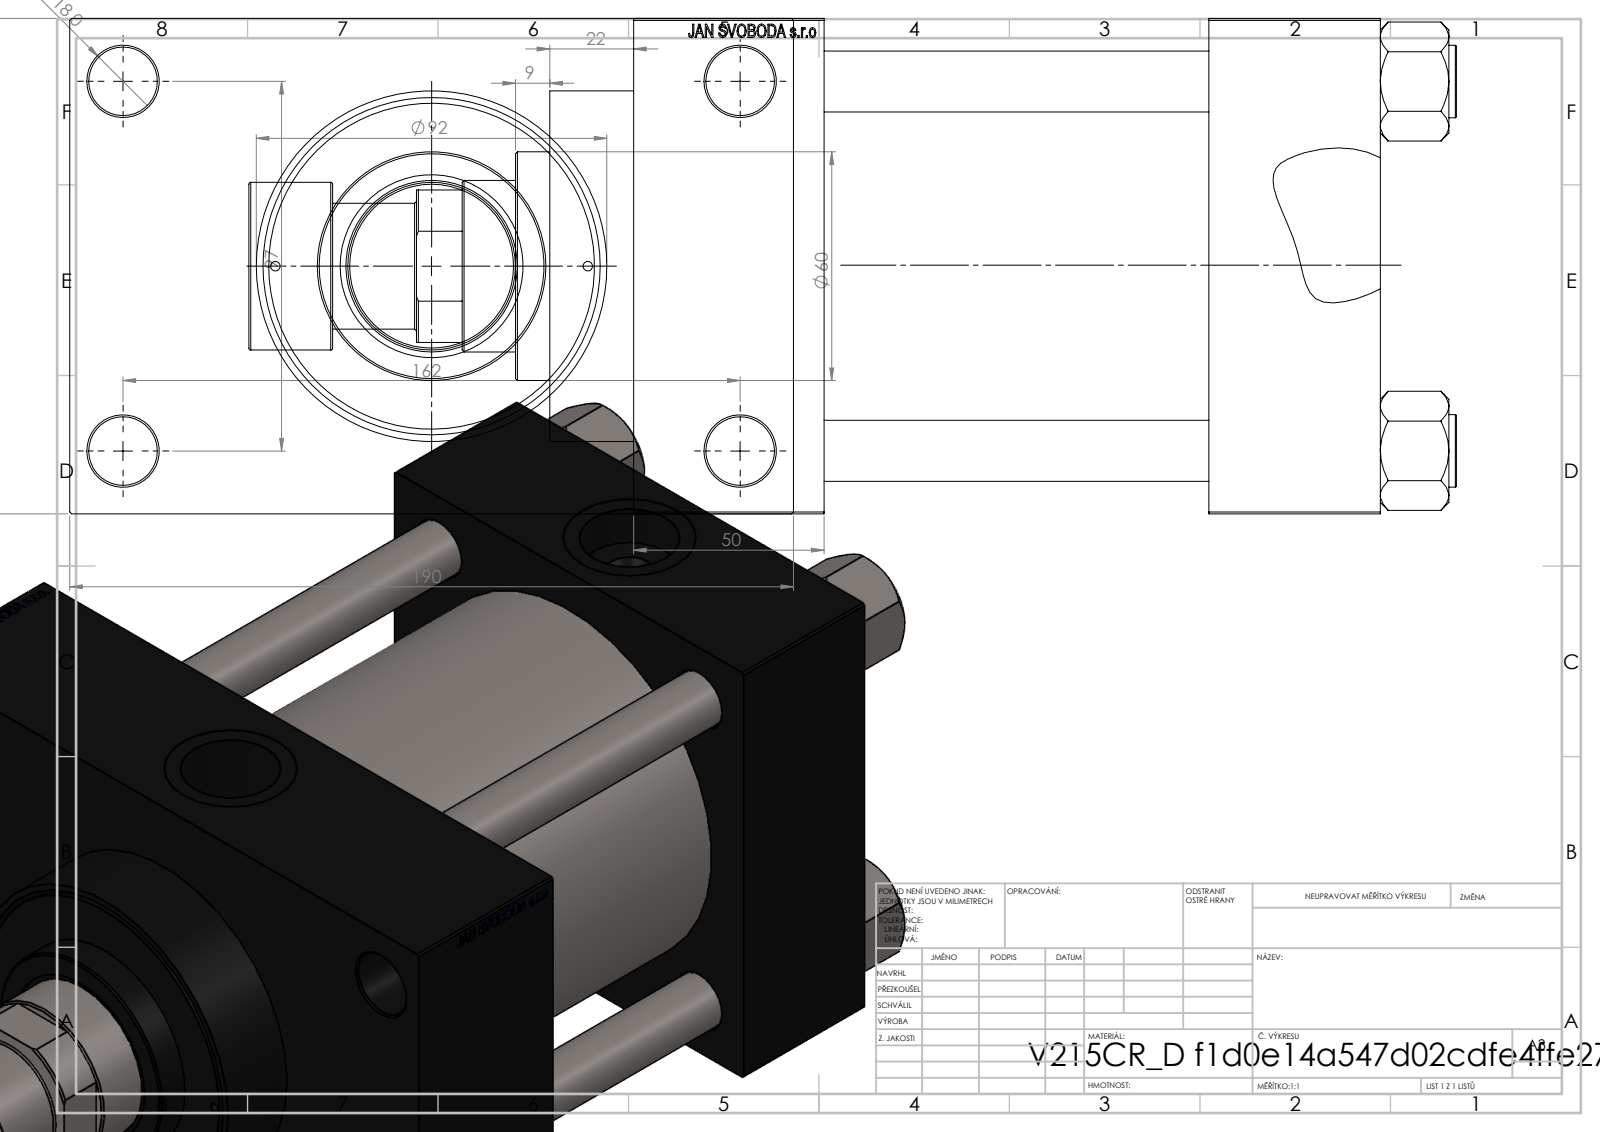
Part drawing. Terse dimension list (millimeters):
name: V215CR_ROD_END_F; V215CR_VCP_D; NUT_M5_D; V215CR_D_Body (+2 more)
written by: SolidWorks 2019 (CONFIG_CONTROL_DESIGN)
unit: mm
bodies: 12 solids, 1173 faces (550 planar, 97 cylindrical, 526 other)
size: 317 × 190 × 130
volume: 2 760 000 mm³; area: 390 306 mm²
holes: 4× ⌀16, 4× ⌀18, 2× ⌀2.5, 2× ⌀7, 2× ⌀26.44, 2× ⌀35, 1× ⌀31.5, 1× ⌀45, 1× ⌀48, 1× ⌀76, 1× ⌀85.5, 1× ⌀100
bosses: 4× ⌀19, 1× ⌀106, 1× ⌀92, 1× ⌀60, 1× ⌀44, 1× ⌀33
face distances: 50, 130, 101, 151, 45, 146, 196, 30, 160, 190
hole spacings: 32.55, 49.02, 62.87, 68.52, 94.41, 96.9, 101.73, 102.27
